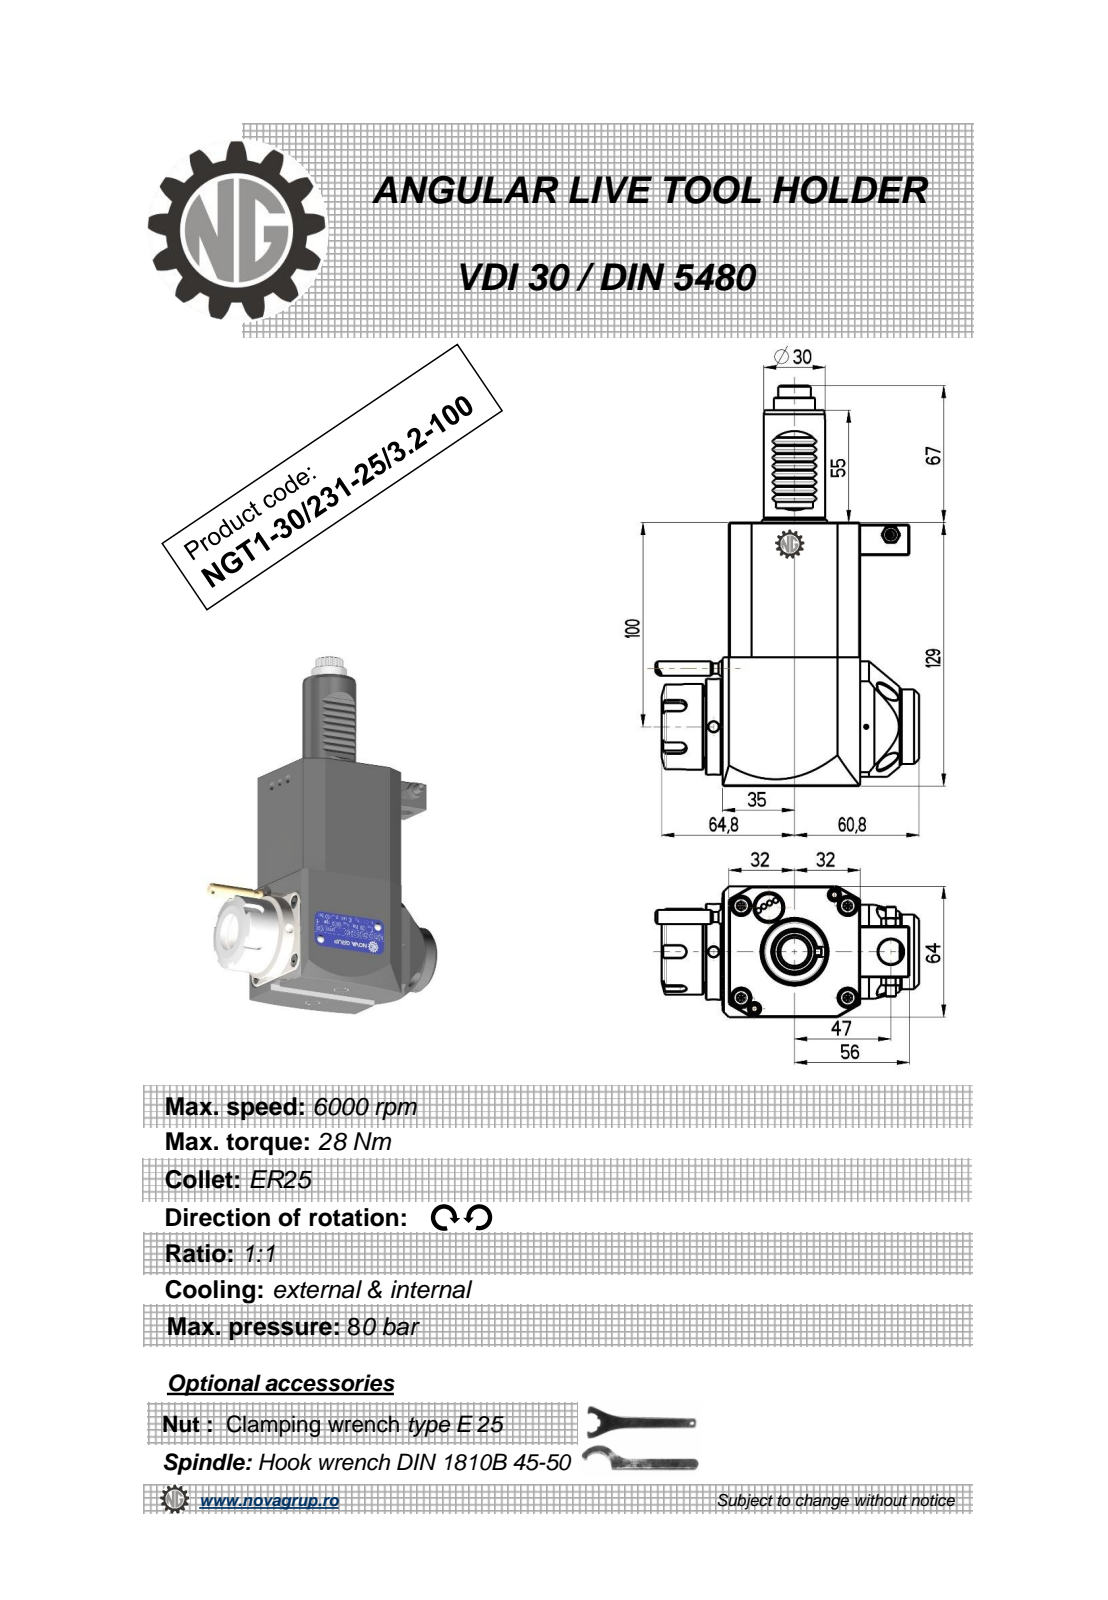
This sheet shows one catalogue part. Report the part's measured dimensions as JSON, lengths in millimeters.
{"part_name": "NGT1_30_231_25_3_2_100", "step_written_by": "PRO/ENGINEER BY PARAMETRIC TECHNOLOGY CORPORATION, 2010280 (CONFIG_CONTROL_DESIGN)", "units": "millimeters", "bodies": {"solids": 1, "faces": 507, "planar": 186, "cylindrical": 155, "other": 166}, "overall_size": [196, 128.63, 64], "volume_mm3": 658666, "surface_area_mm2": 60352, "round_holes": [[5, 2], [2.5, 1], [3, 1], [4.2, 1], [9.5, 1], [12, 1], [20.3, 1]], "round_bosses_or_shafts": [[8.96, 2], [5, 2], [47, 1], [42, 1], [36.5, 1], [35, 1], [30, 1], [20, 1]], "partial_cylinders_radius": [[1.98, 36], [0.26, 12], [0.3, 8], [3, 5], [160, 2], [7.08, 1], [7.92, 1], [13, 1]], "face_to_face_distances": [64, 129, 76.42, 0.5, 3.2, 67.2, 67, 7.5, 3, 8], "hole_center_spacings": [33.19, 65.25, 86.45, 91.5, 127.71]}
